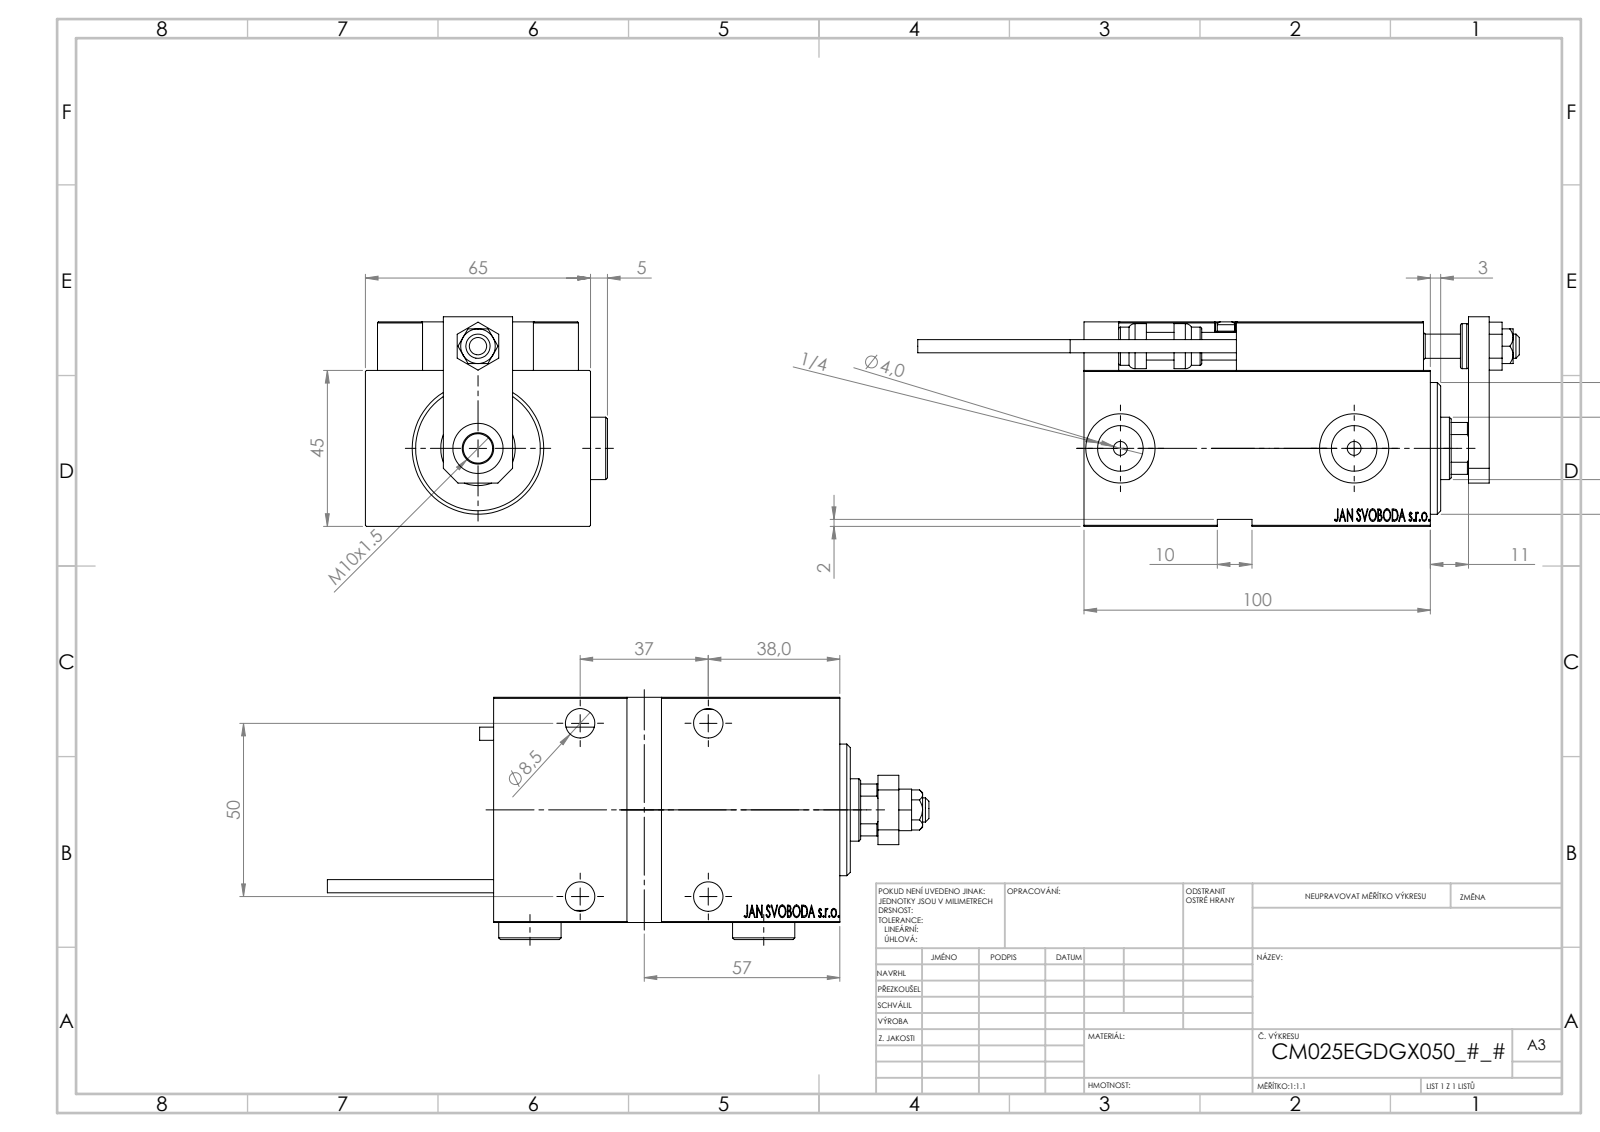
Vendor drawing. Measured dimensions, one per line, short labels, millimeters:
name: KONCOVKA; NUT_D12; SWITCH DIM B,W; V450CM_E_Body (+7 more)
written by: SolidWorks 2019 (CONFIG_CONTROL_DESIGN)
unit: mm
bodies: 26 solids, 1347 faces (604 planar, 198 cylindrical, 545 other)
size: 173.7 × 69.9 × 60.5
volume: 312 701 mm³; area: 81 599 mm²
holes: 6× ⌀4, 5× ⌀8, 5× ⌀8.5, 4× ⌀3.2, 4× ⌀13.5, 2× ⌀5, 2× ⌀13.16, 2× ⌀20, 1× ⌀7, 1× ⌀14.5, 1× ⌀18, 1× ⌀21.5
bosses: 2× ⌀18, 2× ⌀5, 2× ⌀3.8, 1× ⌀38, 1× ⌀27, 1× ⌀13, 1× ⌀11
rounds: 30× R0.3, 2× R3, 1× R8.5
face distances: 45, 65, 14, 59, 6, 13, 5, 100, 3.5, 111
hole spacings: 40.31, 11.37, 20, 25, 29.59, 29.69, 34.44, 36.06
